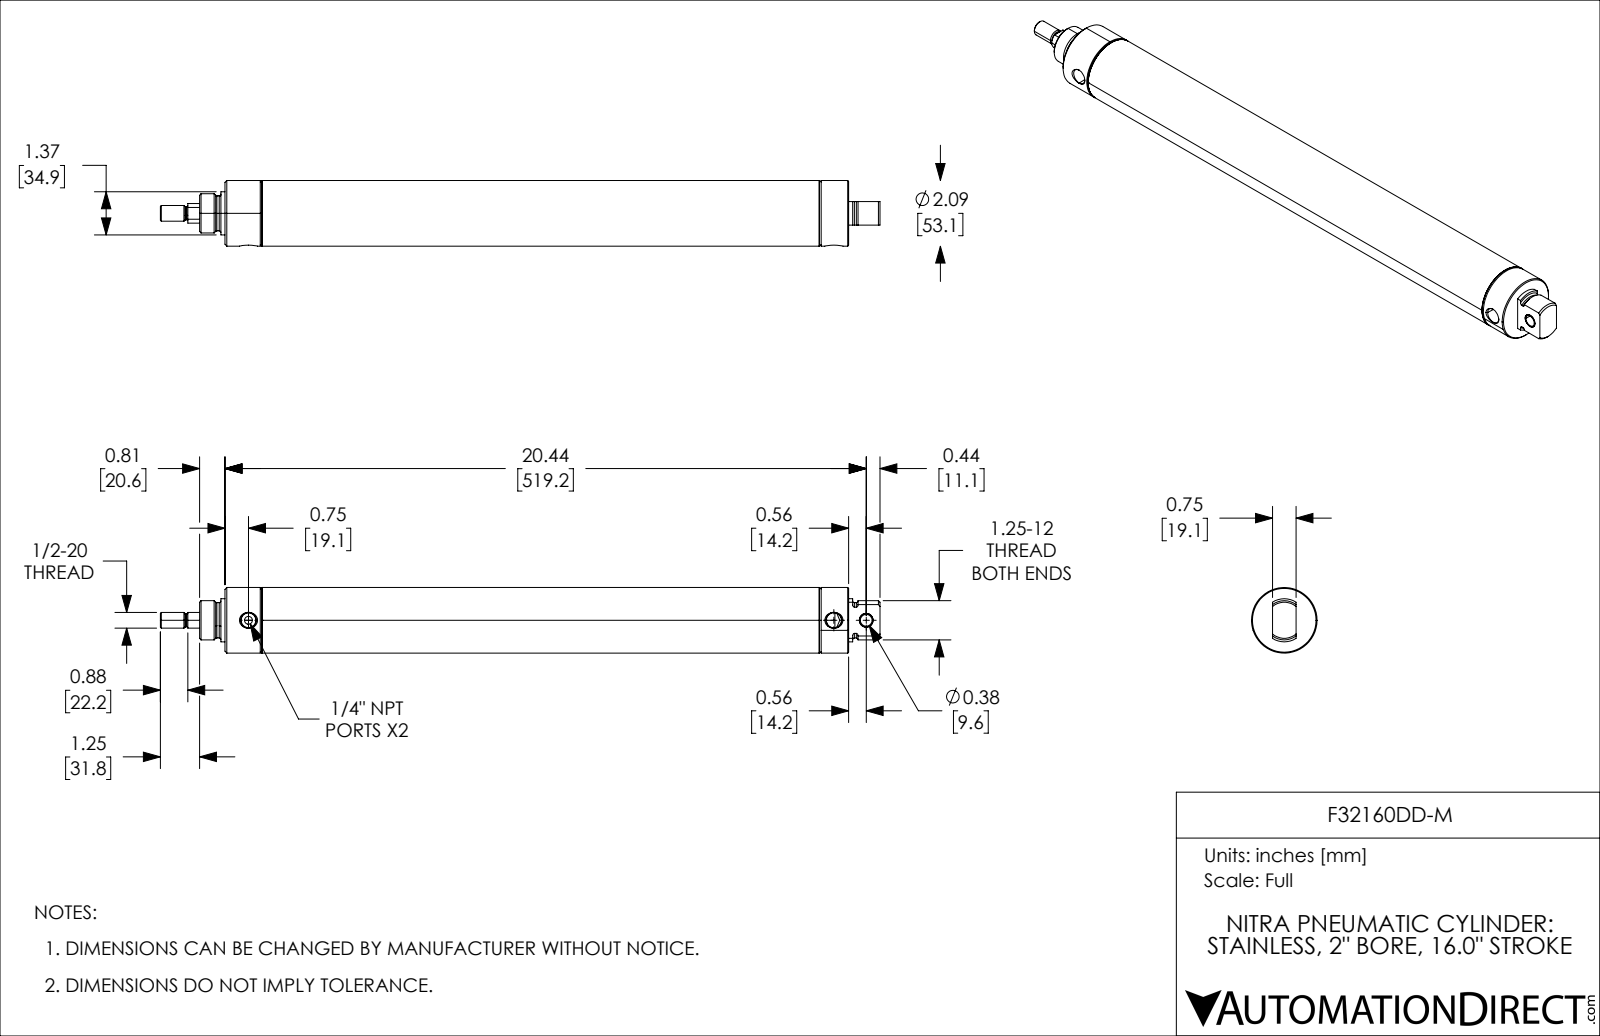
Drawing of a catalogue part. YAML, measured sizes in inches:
part_name: "F32160DD-M_7; F32160DD-M_9; F32160DD-M; F32160DD-M_3 (+2 more)"
step_written_by: "SolidWorks 2021 (CONFIG_CONTROL_DESIGN)"
units: inches
bodies: {solids: 5, faces: 160, planar: 31, cylindrical: 60, other: 69}
overall_size: [22.938, 2.09, 2.09]
volume: 23.22
surface_area: 333.9
round_holes:
  - {diameter: 0.25, count: 1}
  - {diameter: 0.376, count: 1}
  - {diameter: 0.439, count: 1}
  - {diameter: 0.48, count: 1}
  - {diameter: 0.65, count: 1}
  - {diameter: 0.75, count: 1}
  - {diameter: 1.931, count: 1}
round_bosses_or_shafts:
  - {diameter: 2.09, count: 1}
  - {diameter: 2.014, count: 1}
  - {diameter: 1.373, count: 1}
  - {diameter: 1.25, count: 1}
  - {diameter: 1.122, count: 1}
  - {diameter: 0.625, count: 1}
  - {diameter: 0.5, count: 1}
  - {diameter: 0.439, count: 1}
partial_cylinders:
  - {radius: 0.561, count: 1}
face_to_face_distances: [1.188, 16, 17.188, 18.378, 2.378, 1.19, 17.188, 1.188, 1.19, 1.502]
hole_center_spacings: [1.03, 1.03, 18.66, 19.69, 19.69]
